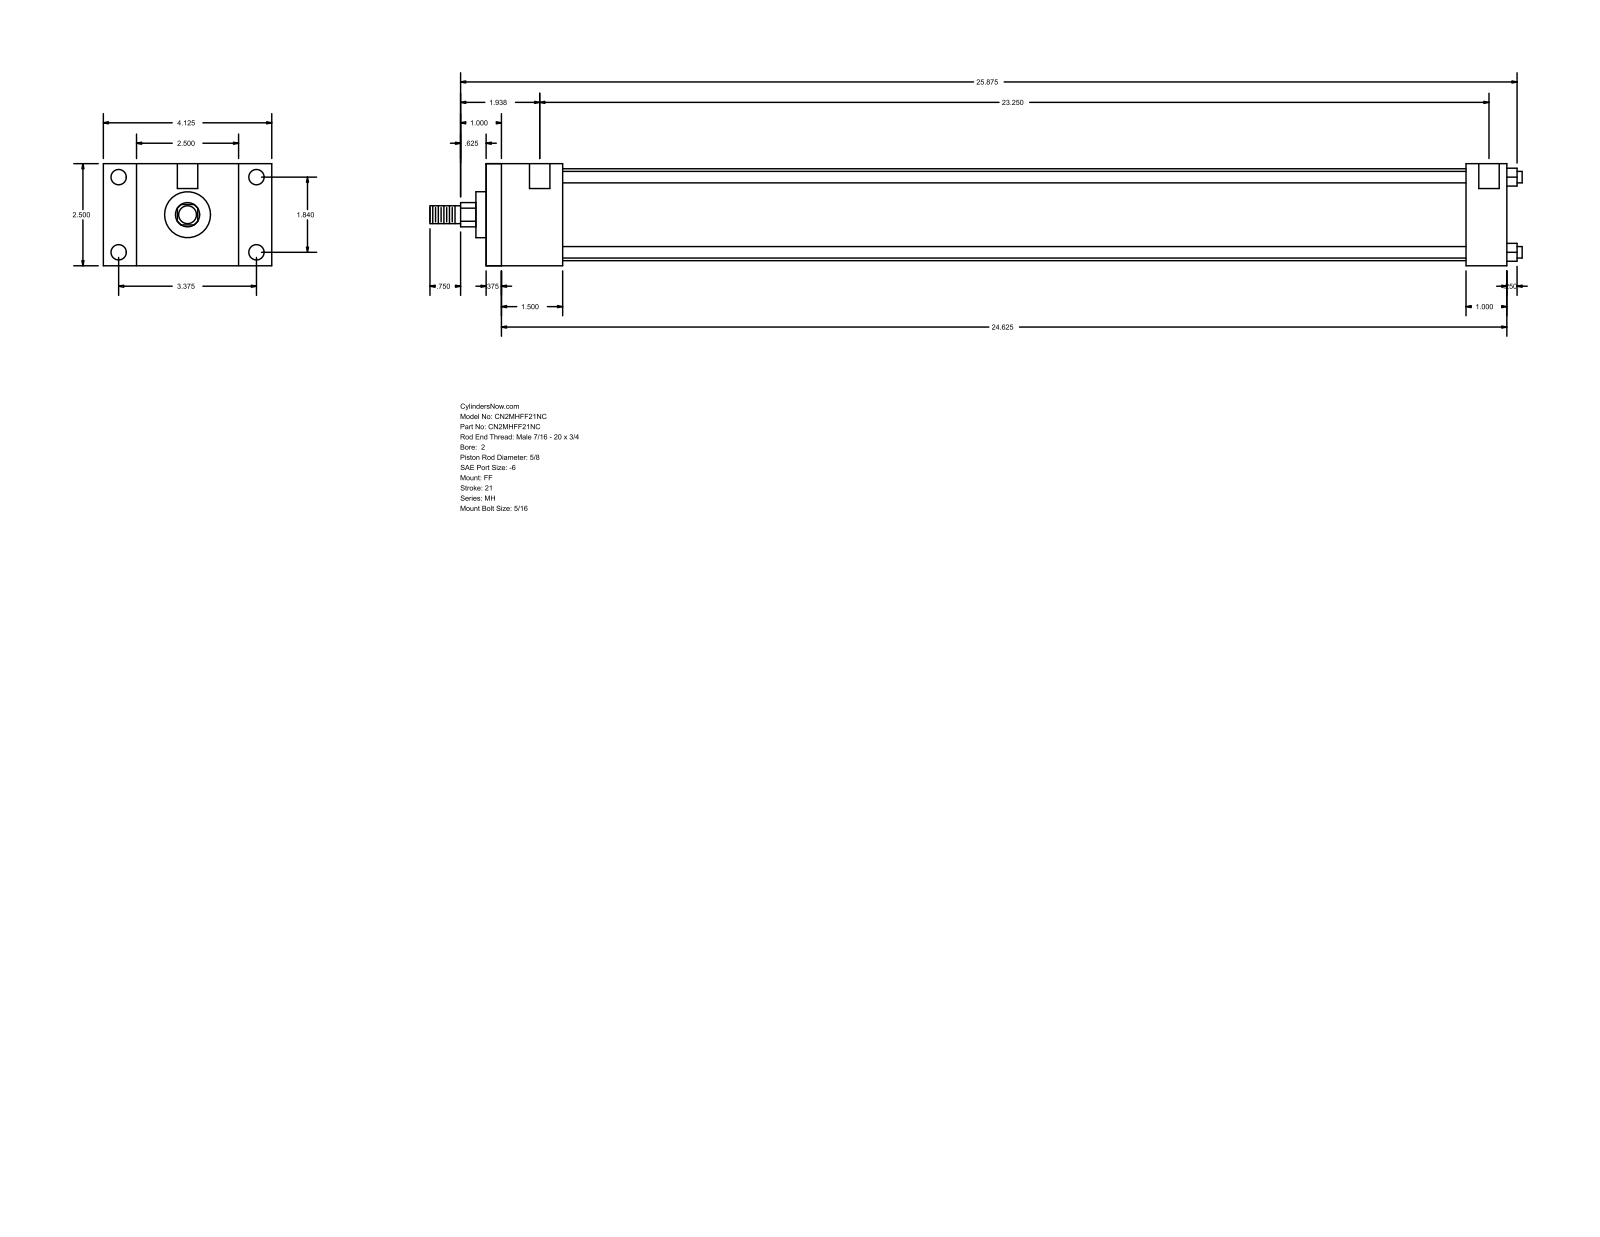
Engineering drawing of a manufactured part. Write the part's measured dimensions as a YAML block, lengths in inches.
part_name: "MH_FF__0200_0.625"
step_written_by: "GSSL Pune (CONFIG_CONTROL_DESIGN)"
units: inches
bodies: {solids: 0, faces: 92, planar: 64, cylindrical: 28, other: 0}
overall_size: [26.75, 4.125, 2.5]
round_holes:
  - {diameter: 0.219, count: 4}
  - {diameter: 0.375, count: 4}
  - {diameter: 0.5, count: 2}
round_bosses_or_shafts:
  - {diameter: 0.281, count: 4}
  - {diameter: 2.25, count: 1}
  - {diameter: 1.125, count: 1}
  - {diameter: 0.625, count: 1}
  - {diameter: 0.437, count: 1}
partial_cylinders:
  - {radius: 0.297, count: 1}
face_to_face_distances: [2.5, 25, 0.375, 24.625, 1, 1.5, 1.875, 24, 23.625, 22.125]
hole_center_spacings: [1.84, 3.375, 3.844, 23.563, 0.125, 0.187, 23.25, 23.375]
